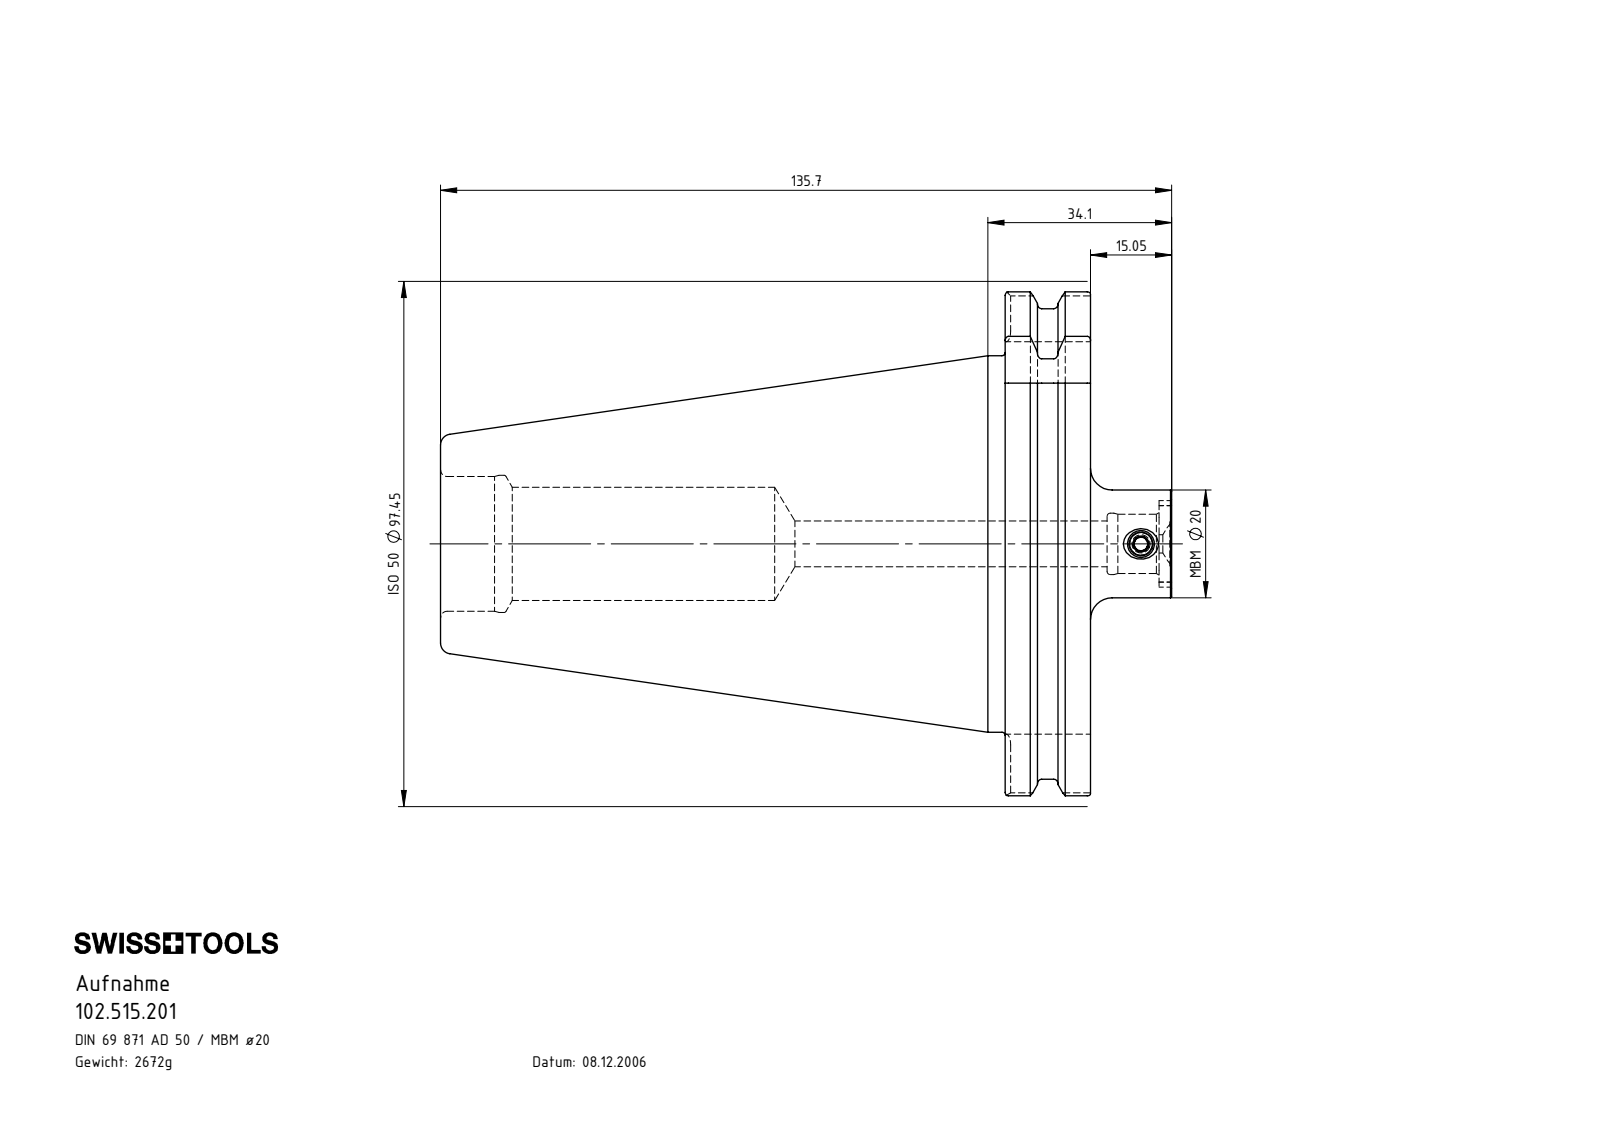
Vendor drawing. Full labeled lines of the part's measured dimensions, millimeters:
Part name (STEP PRODUCT): MB1-ER1.001.006_A; SK5-MB1.K01.034_B; 102.515.201
STEP written by: SolidWorks 2017 (CONFIG_CONTROL_DESIGN)
Units: millimetres
Bodies: 2 solids, 172 faces (53 planar, 50 cylindrical, 69 other)
Overall size (bounding box): 135.7 × 97.45 × 93.51
Volume: 340 415 mm³ · Surface area: 42 564 mm²
Round holes (diameter × count): ⌀2.5 ×1, ⌀4.2 ×1, ⌀8.5 ×1, ⌀11 ×1, ⌀11.4 ×1, ⌀21 ×1, ⌀25 ×1, ⌀25.45 ×1
Round bosses / shafts (diameter × count): ⌀91 ×1, ⌀69.85 ×1, ⌀20 ×1, ⌀5 ×1
Partial cylindrical surfaces — rounded edges, fillets, slot ends (radius × count): R2 ×8, R2.2 ×4, R6.5 ×1, R8.03 ×1, R48.73 ×1
Main face-to-face distances: 15.85, 104.8, 120.65, 72.8, 25.7, 42.7, 17, 7.65, 65.15, 135.7
